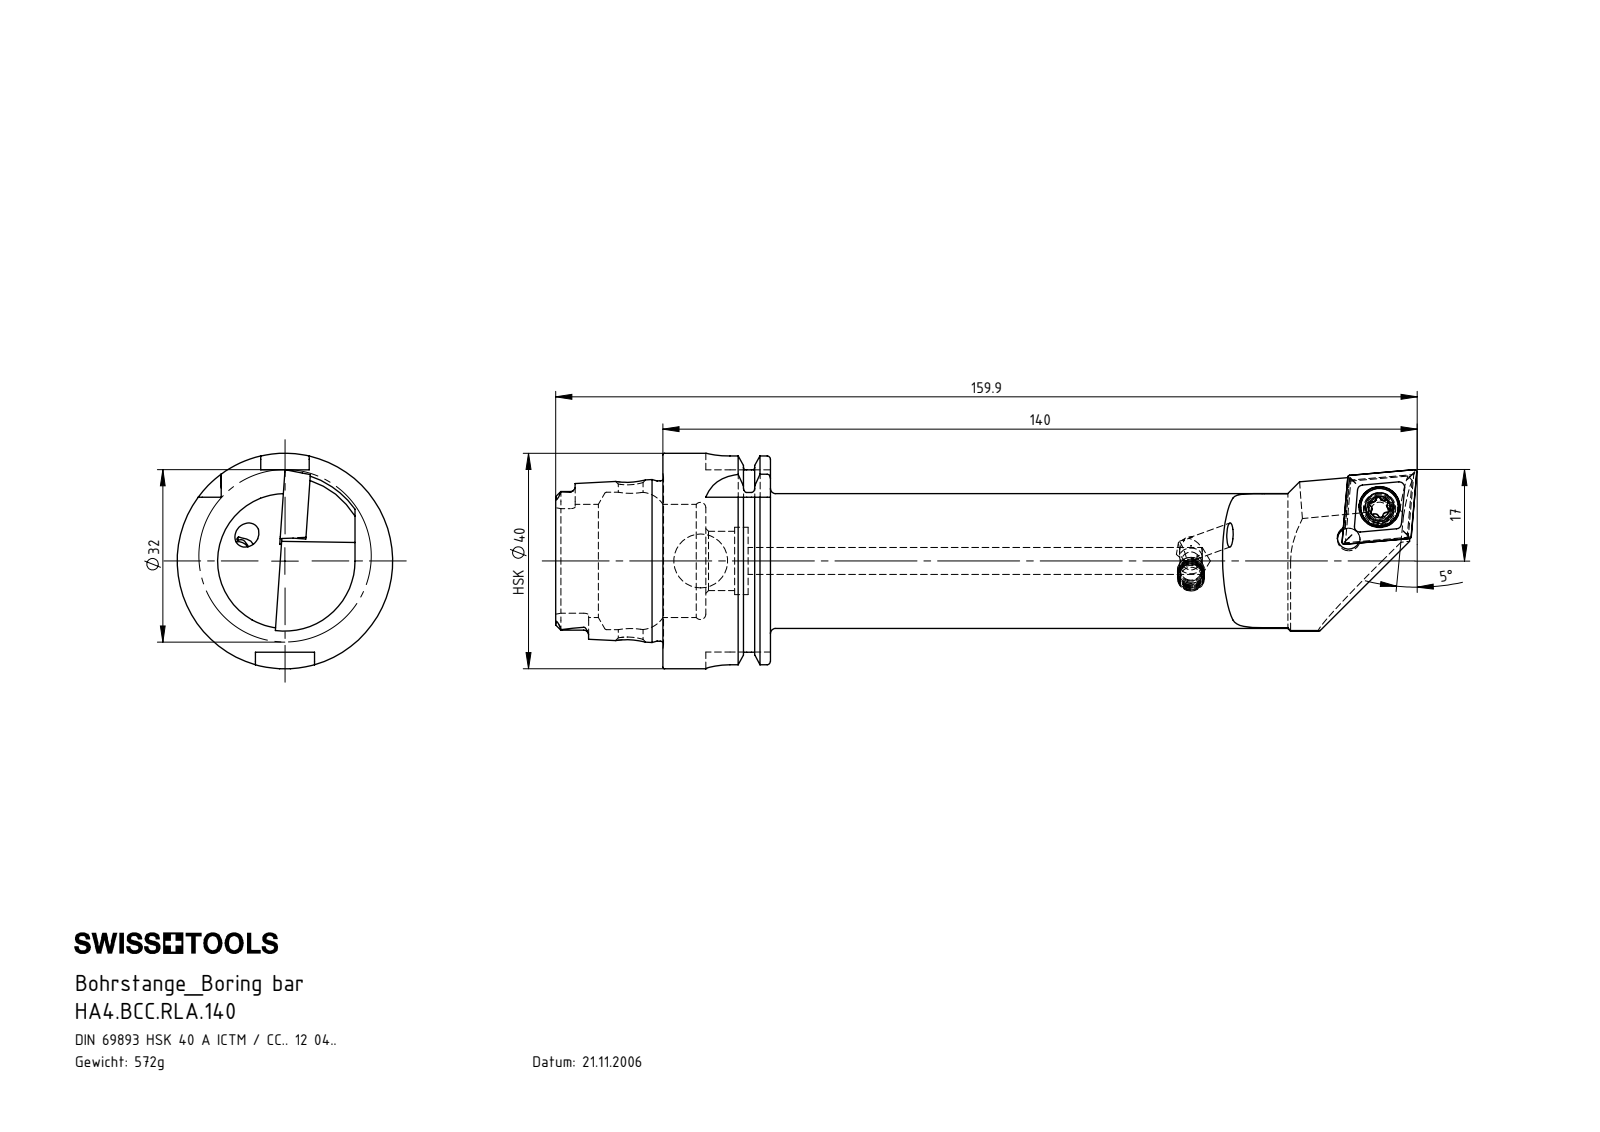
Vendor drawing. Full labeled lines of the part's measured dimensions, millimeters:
Part name (STEP PRODUCT): CCMT120404; WCC-ER2.001.010_A; KVT_MB_600_050; HA4-BCC.RLA.140_B (+1 more)
STEP written by: SolidWorks 2017 (AUTOMOTIVE_DESIGN)
Units: millimetres
Bodies: 6 solids, 318 faces (80 planar, 96 cylindrical, 142 other)
Overall size (bounding box): 159.86 × 40 × 40
Volume: 74 653 mm³ · Surface area: 21 659 mm²
Round holes (diameter × count): ⌀4.2 ×4, ⌀5 ×2, ⌀4 ×1, ⌀4.6 ×1, ⌀5.5 ×1, ⌀7.6 ×1, ⌀10 ×1, ⌀11 ×1, ⌀12.5 ×1, ⌀21 ×1, ⌀25.5 ×1
Round bosses / shafts (diameter × count): ⌀5 ×2, ⌀40 ×1, ⌀34.75 ×1, ⌀29.71 ×1, ⌀25 ×1, ⌀7 ×1
Partial cylindrical surfaces — rounded edges, fillets, slot ends (radius × count): R0.39 ×6, R0.9 ×6, R0.69 ×3, R0.69 ×3, R4.5 ×3, R1.82 ×2, R1.88 ×2, R2.1 ×1
Main face-to-face distances: 19.95, 4.45, 7.95, 12, 19.9, 27.85, 39.85, 35.7, 15.8, 7.85
Hole centre spacings: 7.89, 8.09
